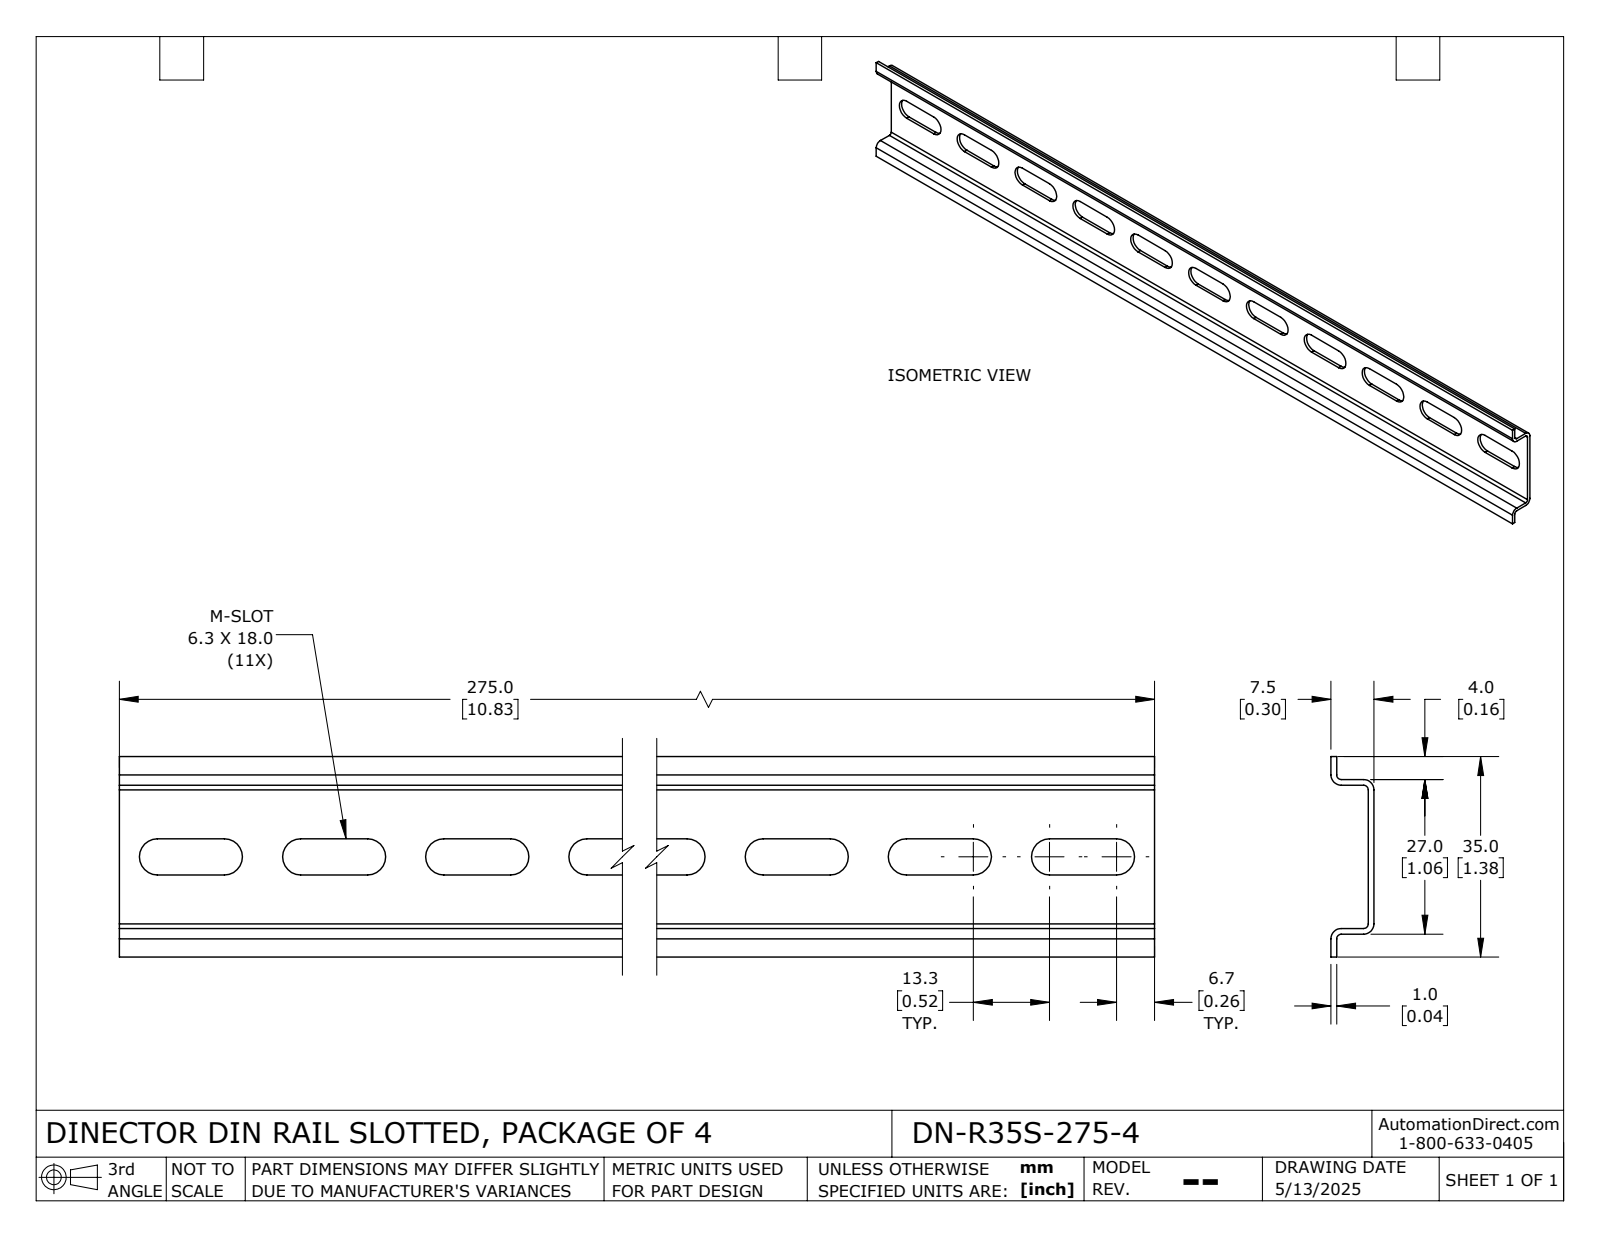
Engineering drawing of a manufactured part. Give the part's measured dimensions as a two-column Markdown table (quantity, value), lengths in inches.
| quantity | value |
| --- | --- |
| part name | DN-R35S-275-4_Default |
| STEP written by | SolidWorks 2024 (CONFIG_CONTROL_DESIGN) |
| units | inches |
| bodies | 1 solid, 66 faces (36 planar, 30 cylindrical, 0 other) |
| overall size | 10.827 × 1.378 × 0.295 |
| volume | 0.698 in³ |
| surface area | 37.17 in² |
| partial cylindrical surfaces (radius × count) | 0.124 × 22, 0.031 × 4, 0.071 × 4 |
| main face-to-face distances | 0.039, 0.256, 1.024, 0.295, 0.217, 0.984, 1.063, 0.157, 0.197, 1.181 |
